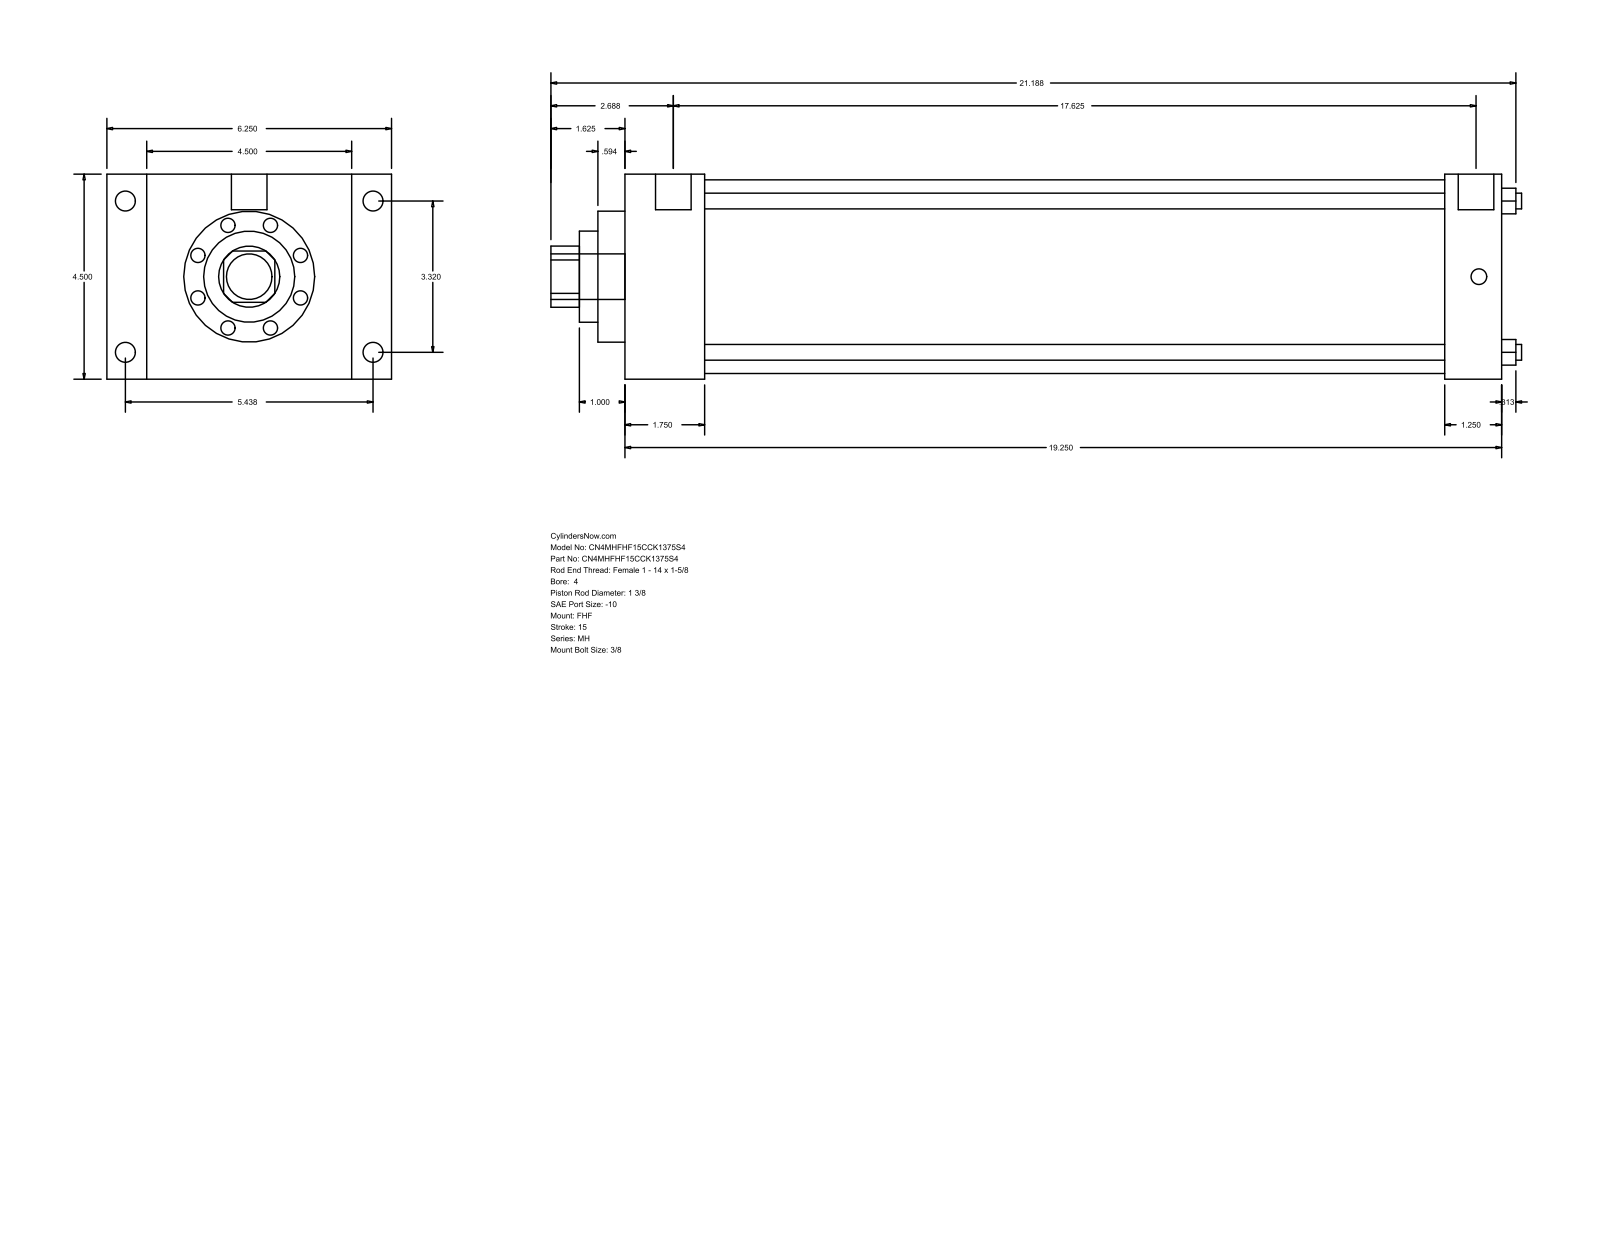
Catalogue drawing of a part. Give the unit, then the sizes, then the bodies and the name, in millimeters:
Units: millimetres
Overall size (bounding box): 541.34 × 158.75 × 114.3
Round holes (diameter × count): ⌀8.76 ×4, ⌀34.92 ×1, ⌀50.8 ×1, ⌀73.03 ×1, ⌀107.95 ×1
Round bosses / shafts (diameter × count): ⌀11.13 ×4, ⌀8.73 ×4, ⌀19.84 ×2, ⌀25.4 ×1
Partial cylindrical surfaces — rounded edges, fillets, slot ends (radius × count): R17.06 ×1
Main face-to-face distances: 114.3, 488.96, 44.45, 444.51, 22.23, 136.53, 158.76, 457.21, 412.76, 31.75
Hole centre spacings: 59.62, 84.32, 119.25
Bodies: 0 solids, 90 faces (61 planar, 29 cylindrical, 0 other)
Part name (STEP PRODUCT): MH_FHF__0400_1.375
STEP written by: GSSL Pune (CONFIG_CONTROL_DESIGN)
